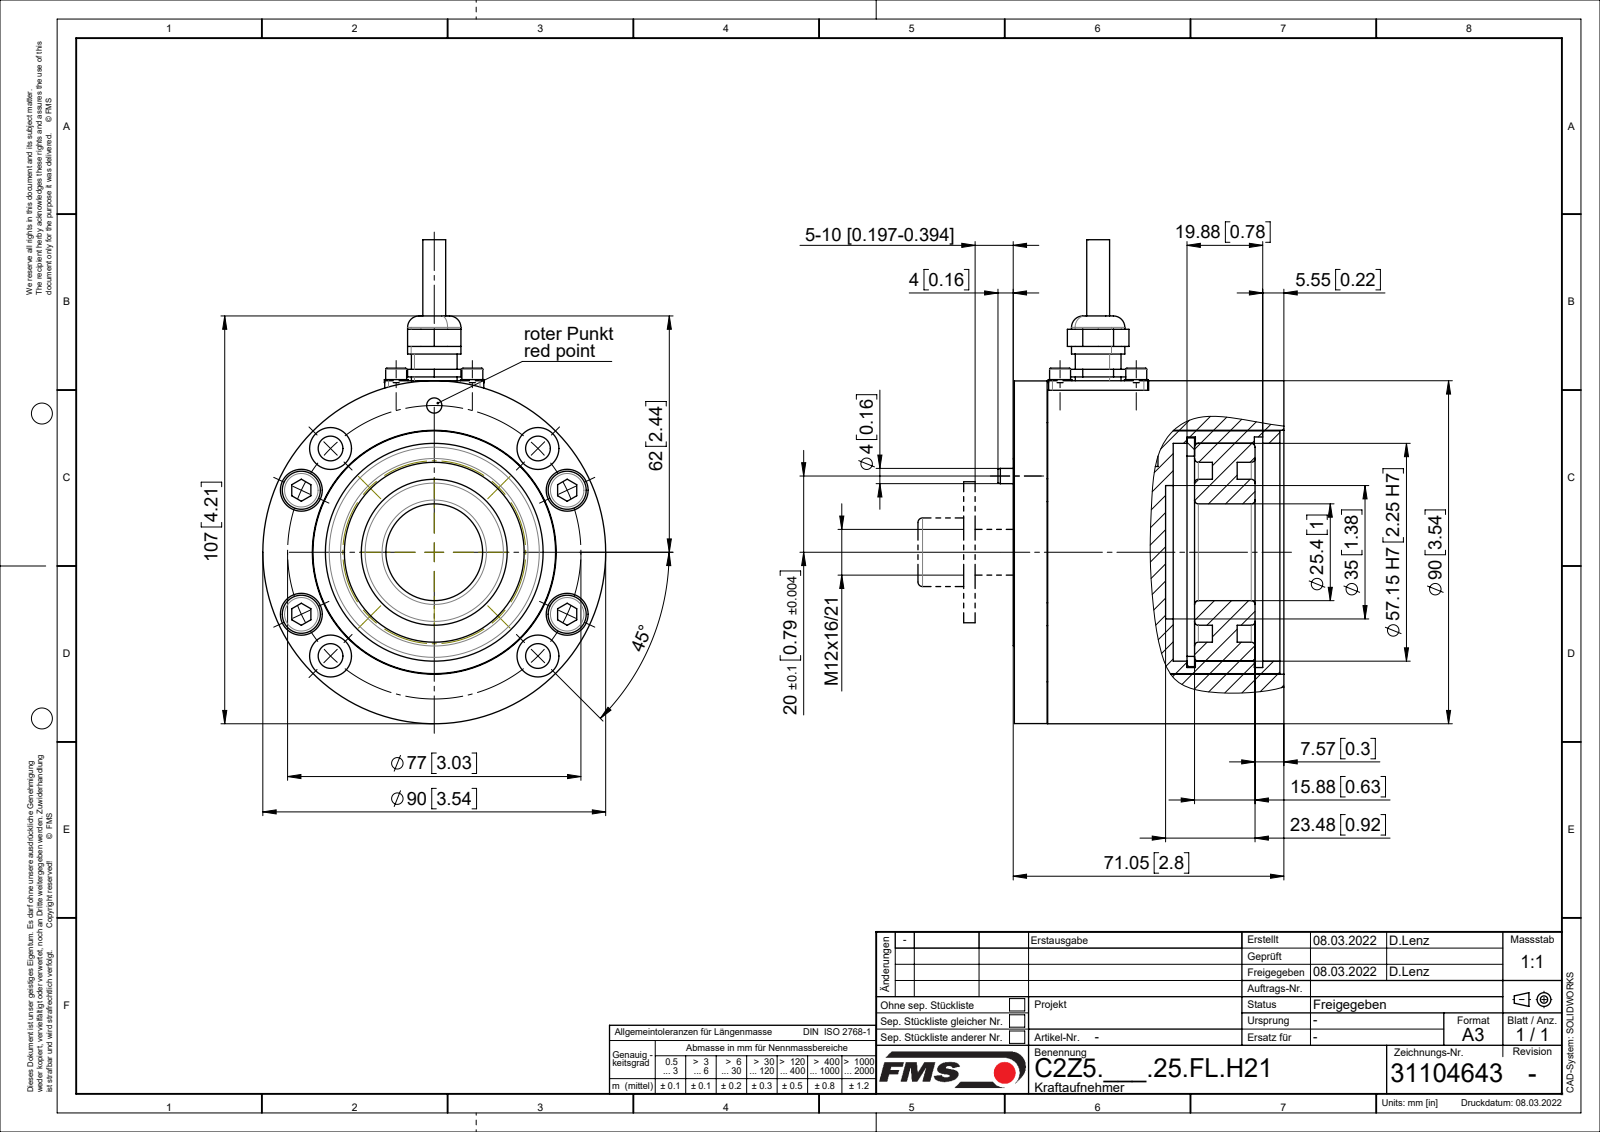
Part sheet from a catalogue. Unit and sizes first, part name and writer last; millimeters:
Units: millimetres
Overall size (bounding box): 127 × 96.05 × 90
Round holes (diameter × count): ⌀6.5 ×8, ⌀11 ×8, ⌀2.5 ×6, ⌀3.1 ×4, ⌀3.4 ×4, ⌀5 ×4, ⌀7 ×4, ⌀4 ×2, ⌀3 ×1, ⌀6 ×1, ⌀10.2 ×1, ⌀12.2 ×1
Round bosses / shafts (diameter × count): ⌀10 ×4, ⌀6.2 ×4, ⌀6 ×4, ⌀5.5 ×4, ⌀3 ×4, ⌀12 ×2, ⌀90 ×1, ⌀89.9 ×1
Partial cylindrical surfaces — rounded edges, fillets, slot ends (radius × count): R0.1 ×4, R1 ×4, R0.5 ×2, R4.16 ×2, R5 ×2, R23.2 ×1, R26.29 ×1
Main face-to-face distances: 6, 33.05, 32, 38, 8.6, 29.1, 37.7, 5.7, 2.9, 28.95
Hole centre spacings: 20, 38.5, 13.37, 14.14, 38.49, 44.16, 54.44, 63.07
Volume: 307 821 mm³ · Surface area: 120 518 mm²
Bodies: 23 solids, 525 faces (201 planar, 228 cylindrical, 96 other)
Part name (STEP PRODUCT): Sch DIN9021_M12; Spannstift_ISO13337_D04x10; Si-Ring DIN472_D57.15; 31104496_stp_01 (+8 more)
STEP written by: SolidWorks 2018 (CONFIG_CONTROL_DESIGN)
